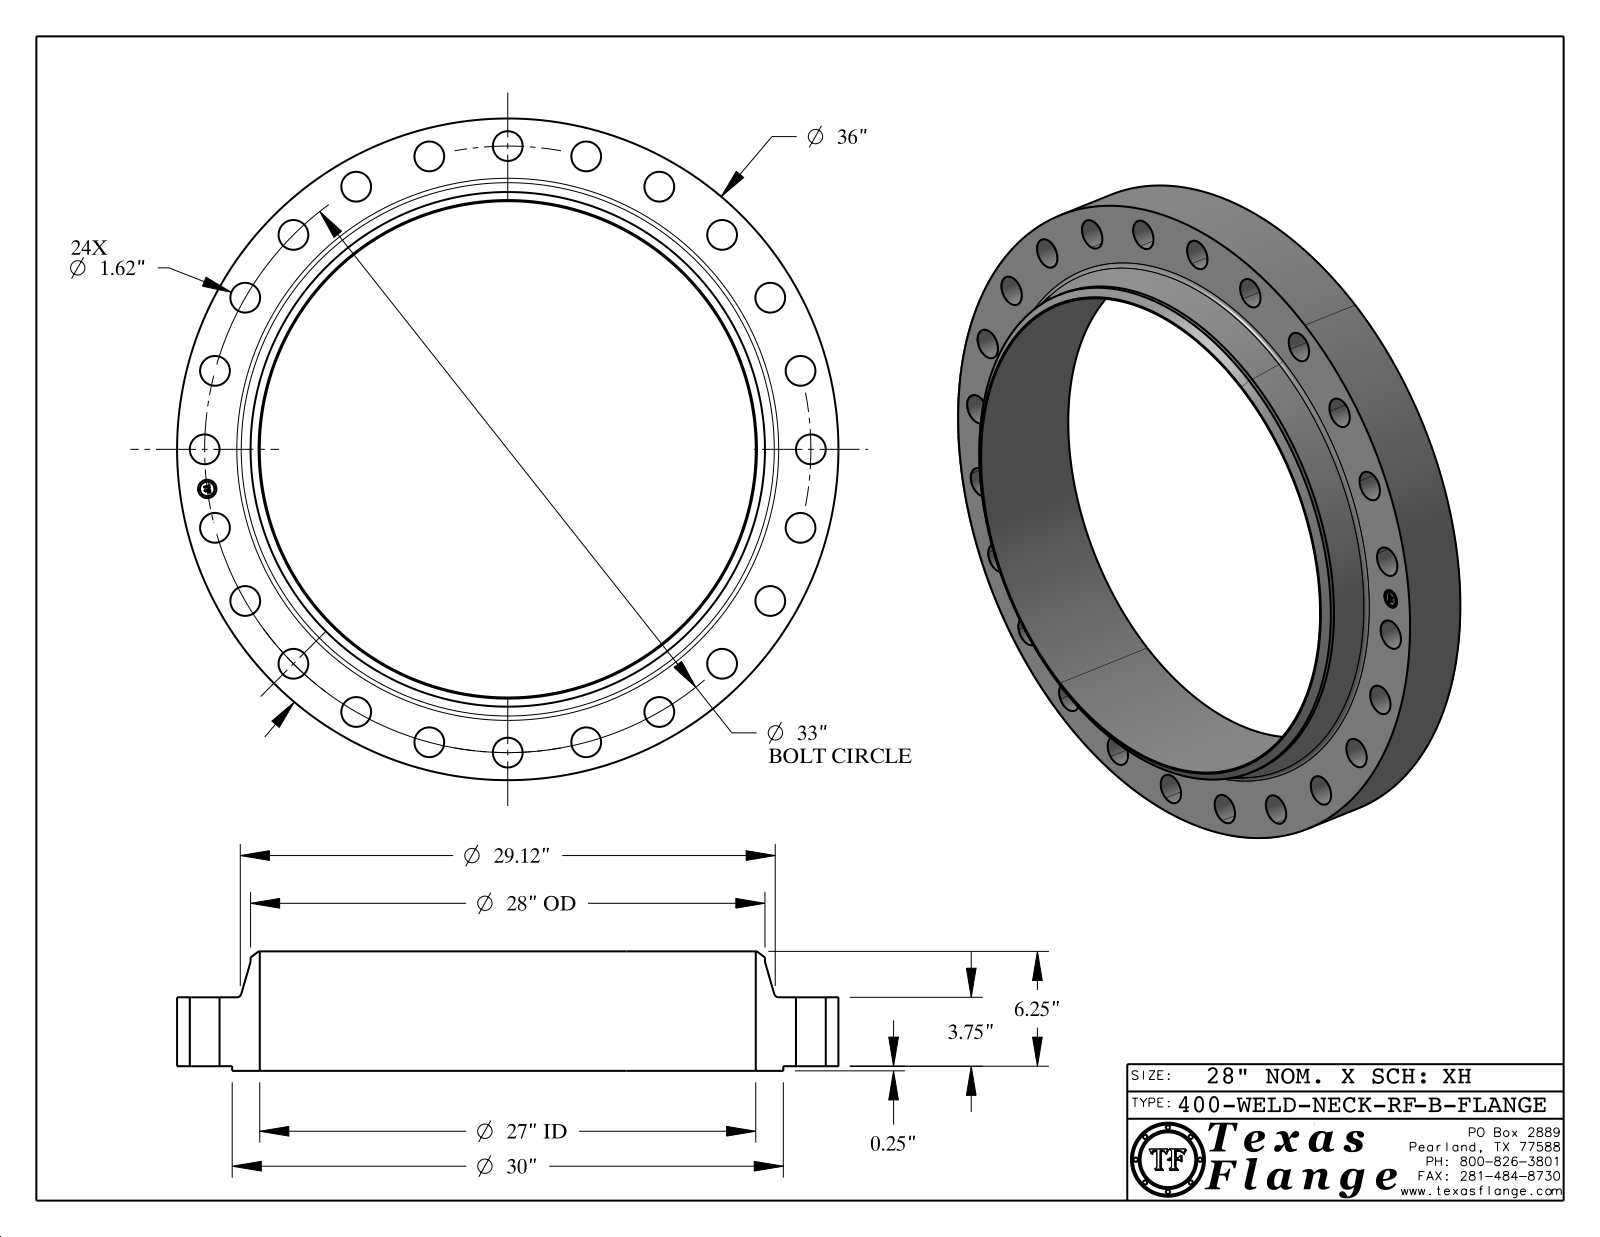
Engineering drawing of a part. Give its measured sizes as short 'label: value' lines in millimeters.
name: 400-WELD-NECK-RF, Series B
written by: CATIA V5 STEP AP214 (AUTOMOTIVE_DESIGN)
unit: mm
bodies: 1 solid, 451 faces (369 planar, 76 cylindrical, 6 other)
size: 914.4 × 914.4 × 165.1
volume: 27 330 000 mm³; area: 1 552 000 mm²
holes: 24× ⌀41.1, 1× ⌀25.4, 1× ⌀685.8
bosses: 8× ⌀1.5, 1× ⌀914.4, 1× ⌀762, 1× ⌀711.2, 1× ⌀20
face distances: 95.3, 6.4, 101.6, 165.1, 158.8, 63.5, 101.2, 94.9, 0.4, 63.9
hole spacings: 419.1, 109.4, 216.9, 510.3, 592.7, 665, 809.7, 831
